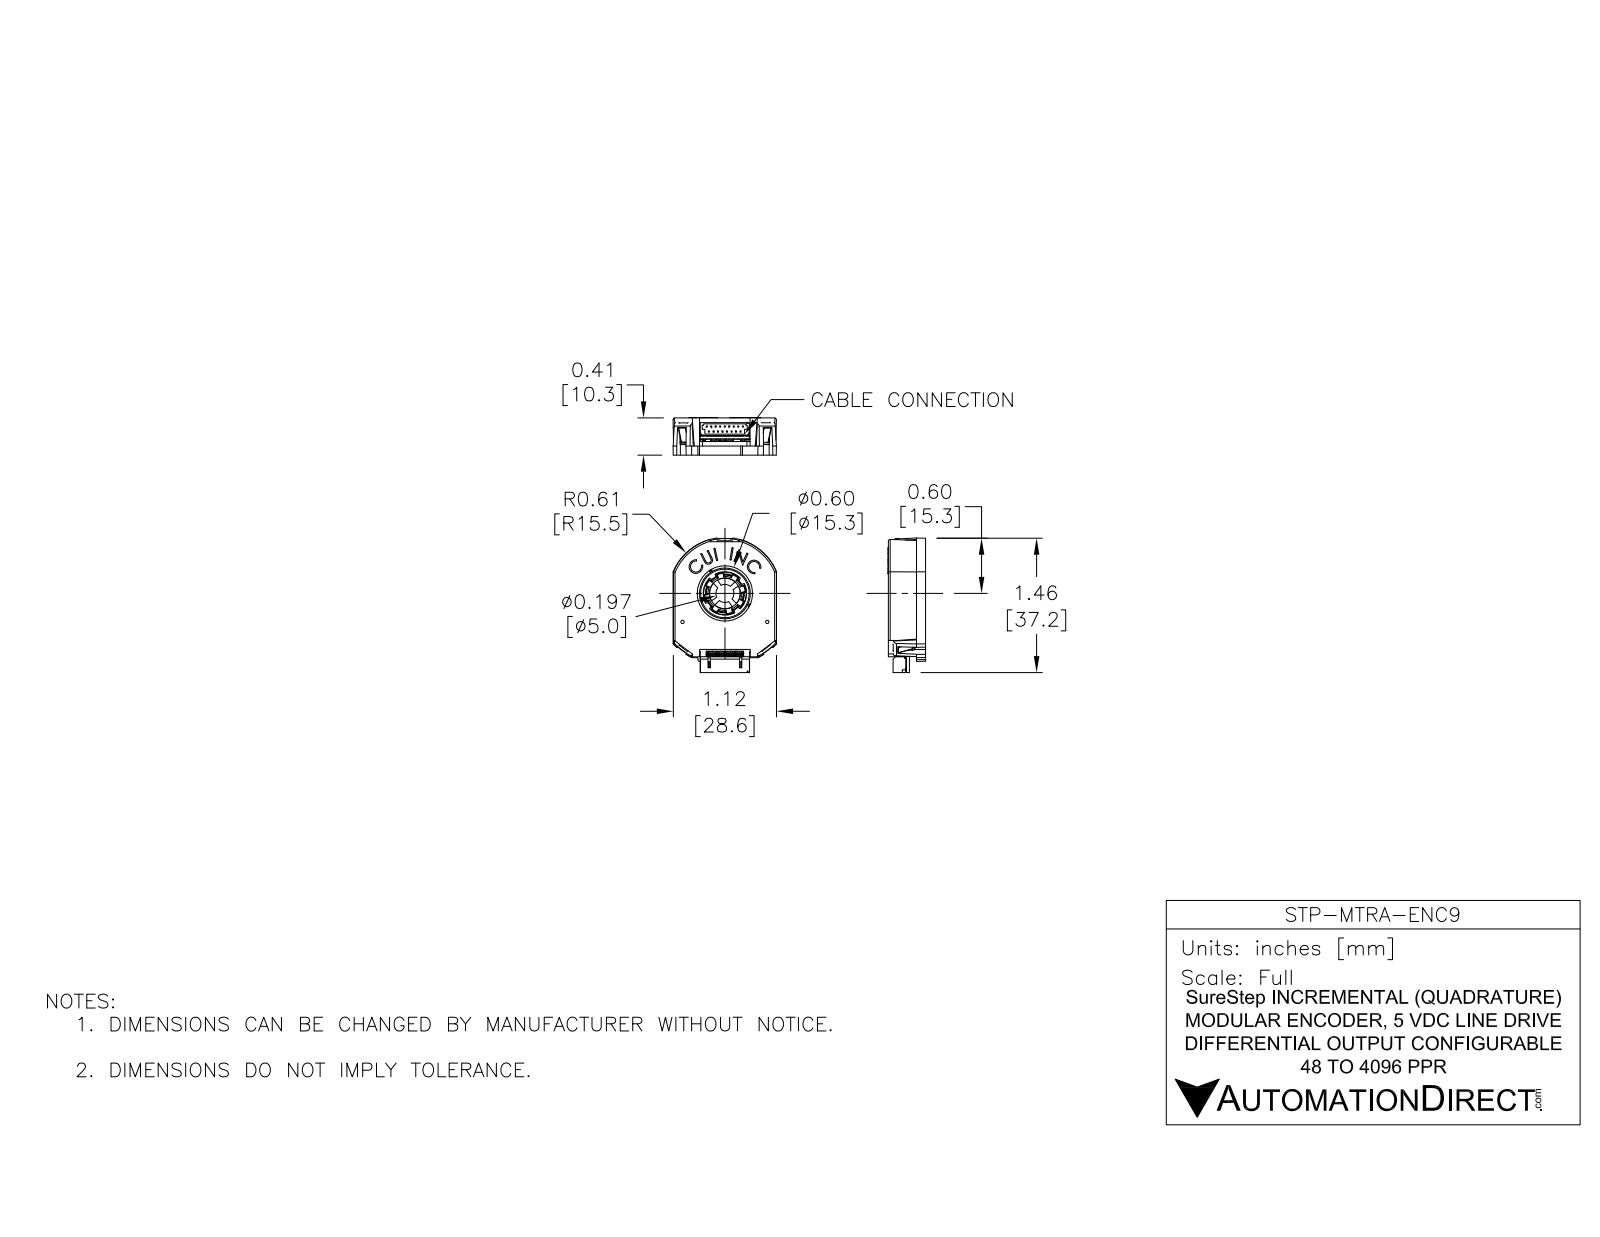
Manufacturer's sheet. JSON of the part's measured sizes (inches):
{"part_name": "STP-MTRA-ENC9", "step_written_by": "SolidWorks 2017 (AUTOMOTIVE_DESIGN)", "units": "inches", "bodies": {"solids": 7, "faces": 1217, "planar": 710, "cylindrical": 278, "other": 229}, "overall_size": [1.467, 1.126, 0.409], "volume_in3": 0.298, "surface_area_in2": 13.44, "round_holes": [[0.031, 4], [0.037, 4], [0.079, 4], [0.067, 2], [0.091, 2], [0.116, 2], [0.161, 2], [0.177, 2], [0.472, 1], [0.496, 1], [0.56, 1], [0.602, 1]], "round_bosses_or_shafts": [[0.059, 4], [0.465, 1], [0.413, 1]], "partial_cylinders_radius": [[0.039, 22], [0.02, 6], [0.041, 6], [0.079, 6], [0.012, 4], [0.016, 4], [0.08, 4], [0.004, 3]], "face_to_face_distances": [0.209, 0.175, 0.033, 0.406, 0.23, 0.197, 0.307, 0.098, 0.077, 0.11], "hole_center_spacings": [0.354, 0.5, 0.707, 0.81, 0.75, 0.078, 0.117, 0.172]}
